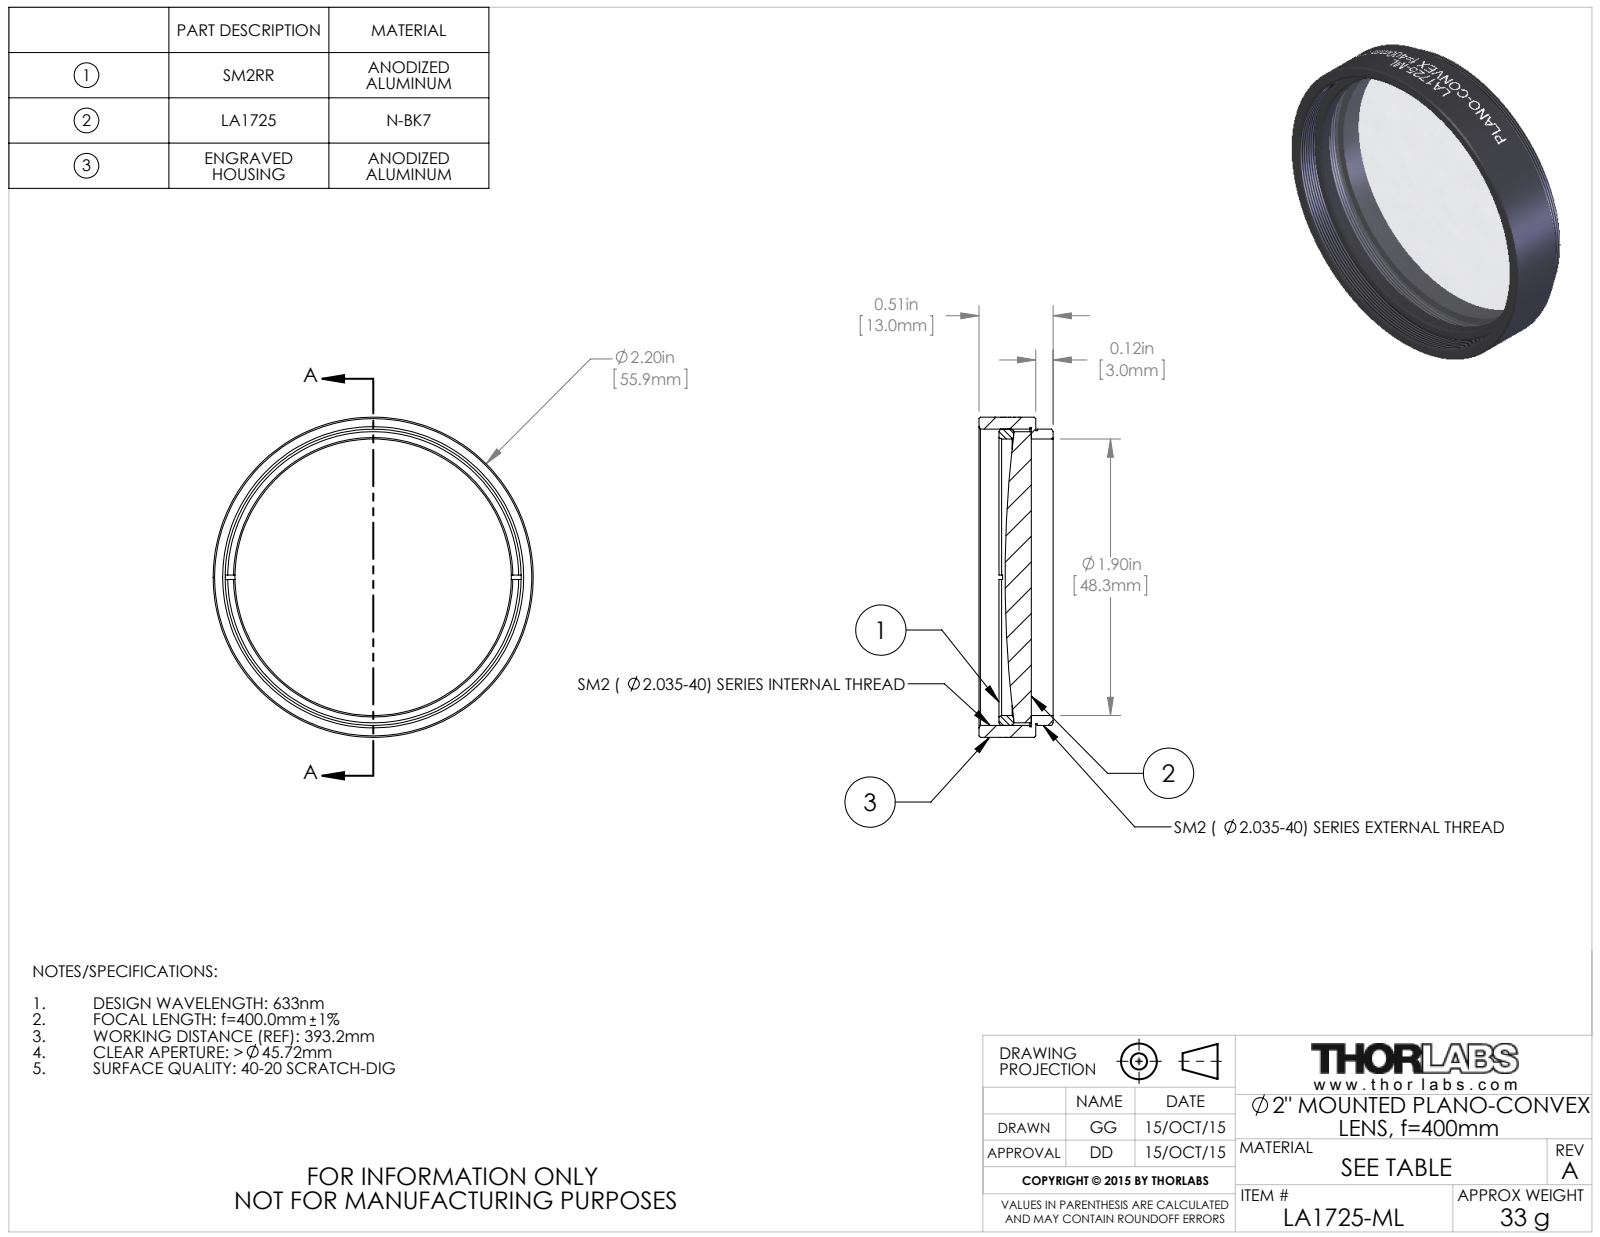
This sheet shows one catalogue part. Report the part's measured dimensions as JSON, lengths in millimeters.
{"part_name": "TTN039606-E0W", "step_written_by": "SolidWorks 2014 (CONFIG_CONTROL_DESIGN)", "units": "millimeters", "bodies": {"solids": 3, "faces": 108, "planar": 16, "cylindrical": 72, "other": 20}, "overall_size": [55.9, 55.9, 13], "volume_mm3": 12800, "surface_area_mm2": 11350, "round_holes": [[48.3, 1], [52.2, 1]], "round_bosses_or_shafts": [[55.9, 1], [51.7, 1], [51.2, 1], [50.8, 1]], "face_to_face_distances": [0.8, 9.9, 9.1, 3, 3.8, 13, 6.9, 3.9, 3.1, 6]}
